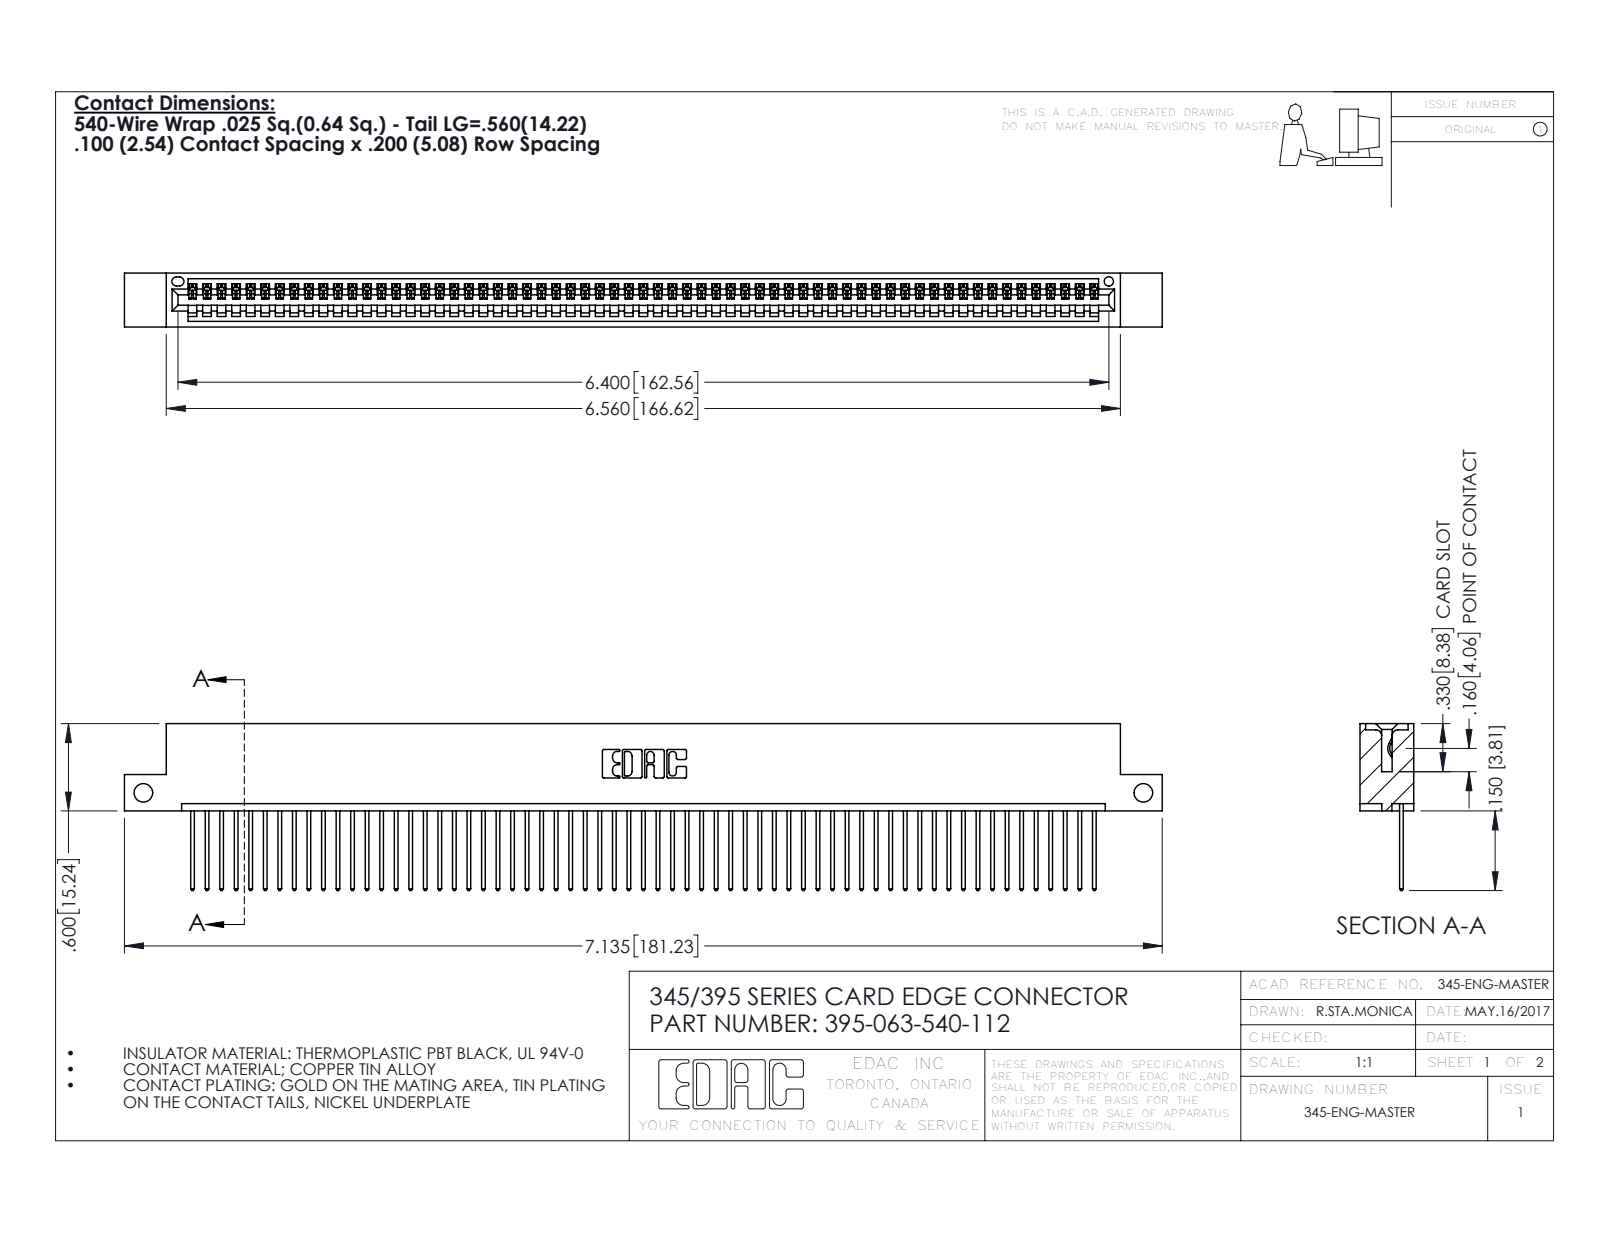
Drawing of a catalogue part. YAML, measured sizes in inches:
part_name: "345-292-001_345-293-140; 395-063-540-112; 345 Part_Flush Mounting Lugs - Side Mount"
step_written_by: "SolidWorks 2016 (CONFIG_CONTROL_DESIGN)"
units: inches
bodies: {solids: 64, faces: 3780, planar: 2600, cylindrical: 1180, other: 0}
overall_size: [7.135, 1.147, 0.37]
volume: 1.061
surface_area: 36.98
round_holes:
  - {diameter: 0.128, count: 2}
  - {diameter: 0.064, count: 1}
partial_cylinders:
  - {radius: 0.006, count: 126}
  - {radius: 0.01, count: 126}
  - {radius: 0.01, count: 22}
  - {radius: 0.007, count: 6}
  - {radius: 0.031, count: 6}
  - {radius: 0.026, count: 3}
  - {radius: 0.031, count: 2}
  - {radius: 0.04, count: 2}
face_to_face_distances: [0.072, 0.298, 0.37, 0.098, 0.272, 0.025, 0.2, 0.225, 0.149, 0.072]
hole_center_spacings: [6.875]
